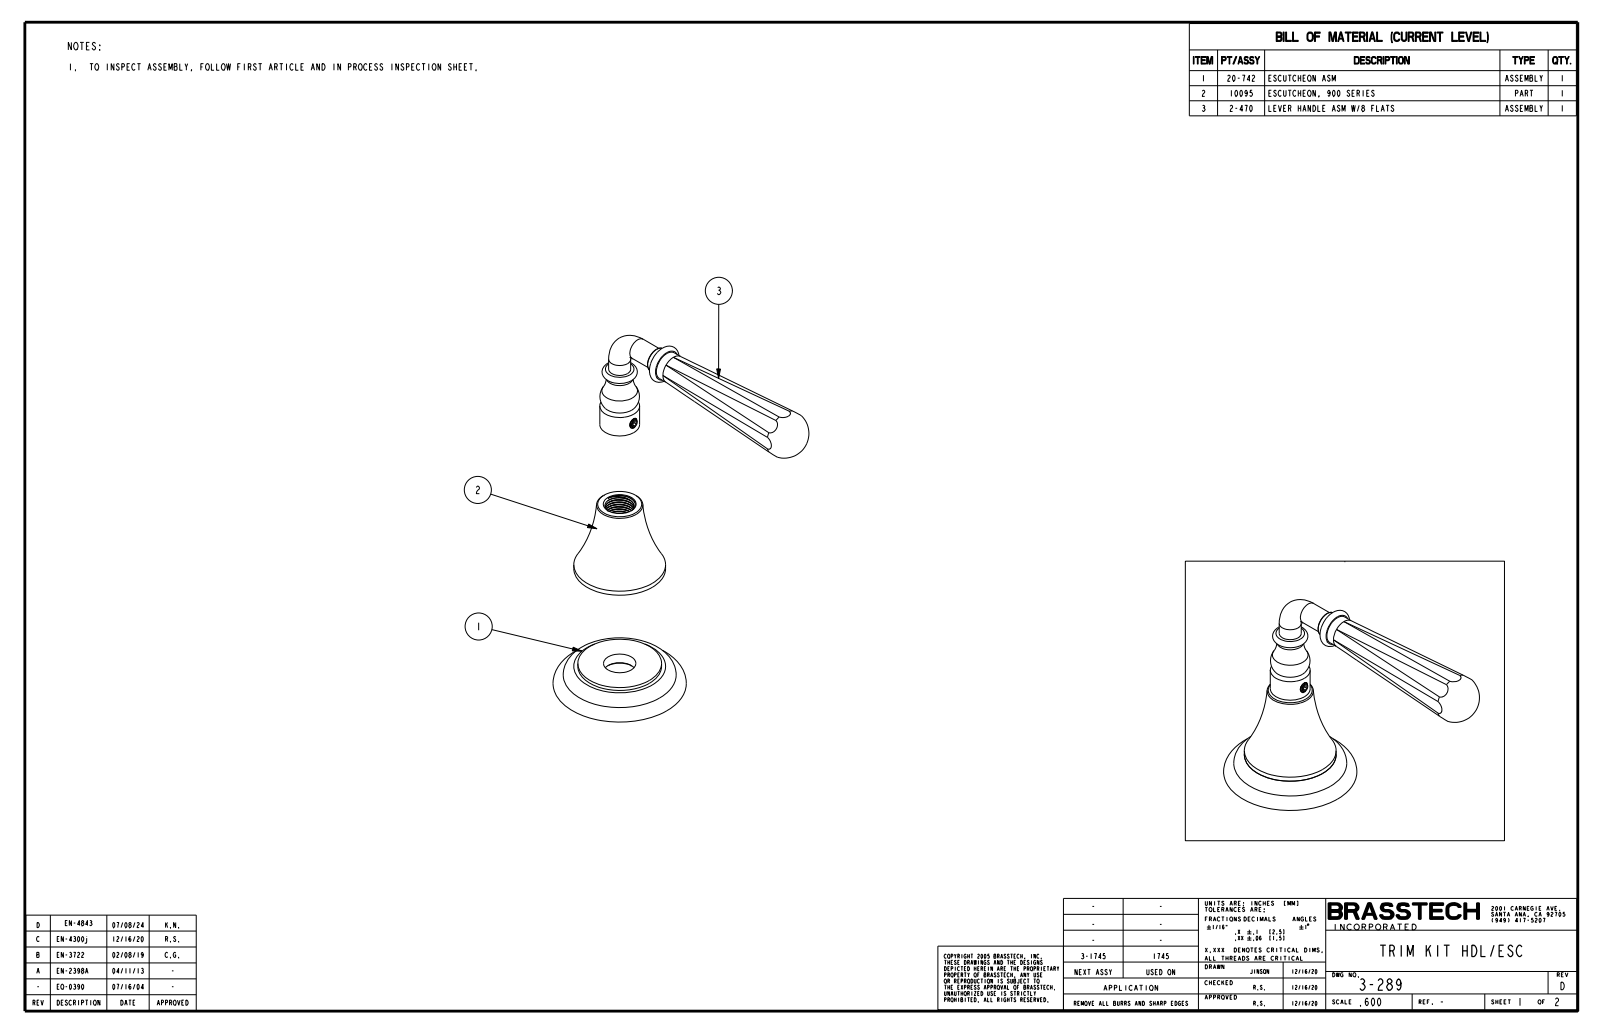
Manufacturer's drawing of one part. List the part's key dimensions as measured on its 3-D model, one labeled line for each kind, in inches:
Part name (STEP PRODUCT): 3-289
STEP written by: CREO PARAMETRIC BY PTC INC, 2018400 (CONFIG_CONTROL_DESIGN)
Units: inches
Bodies: 1 solid, 65 faces (15 planar, 14 cylindrical, 36 other)
Overall size (bounding box): 5.737 × 4.095 × 2.36
Volume: 4.708 in³ · Surface area: 26.72 in²
Round bosses / shafts (diameter × count): ⌀0.39 ×2, ⌀1.625 ×1, ⌀0.705 ×1, ⌀0.525 ×1, ⌀0.475 ×1, ⌀0.4 ×1
Main face-to-face distances: 1.775, 1.805, 0.03, 3.005, 1.23, 1.2, 0.264, 0.375, 1.4, 1.43
